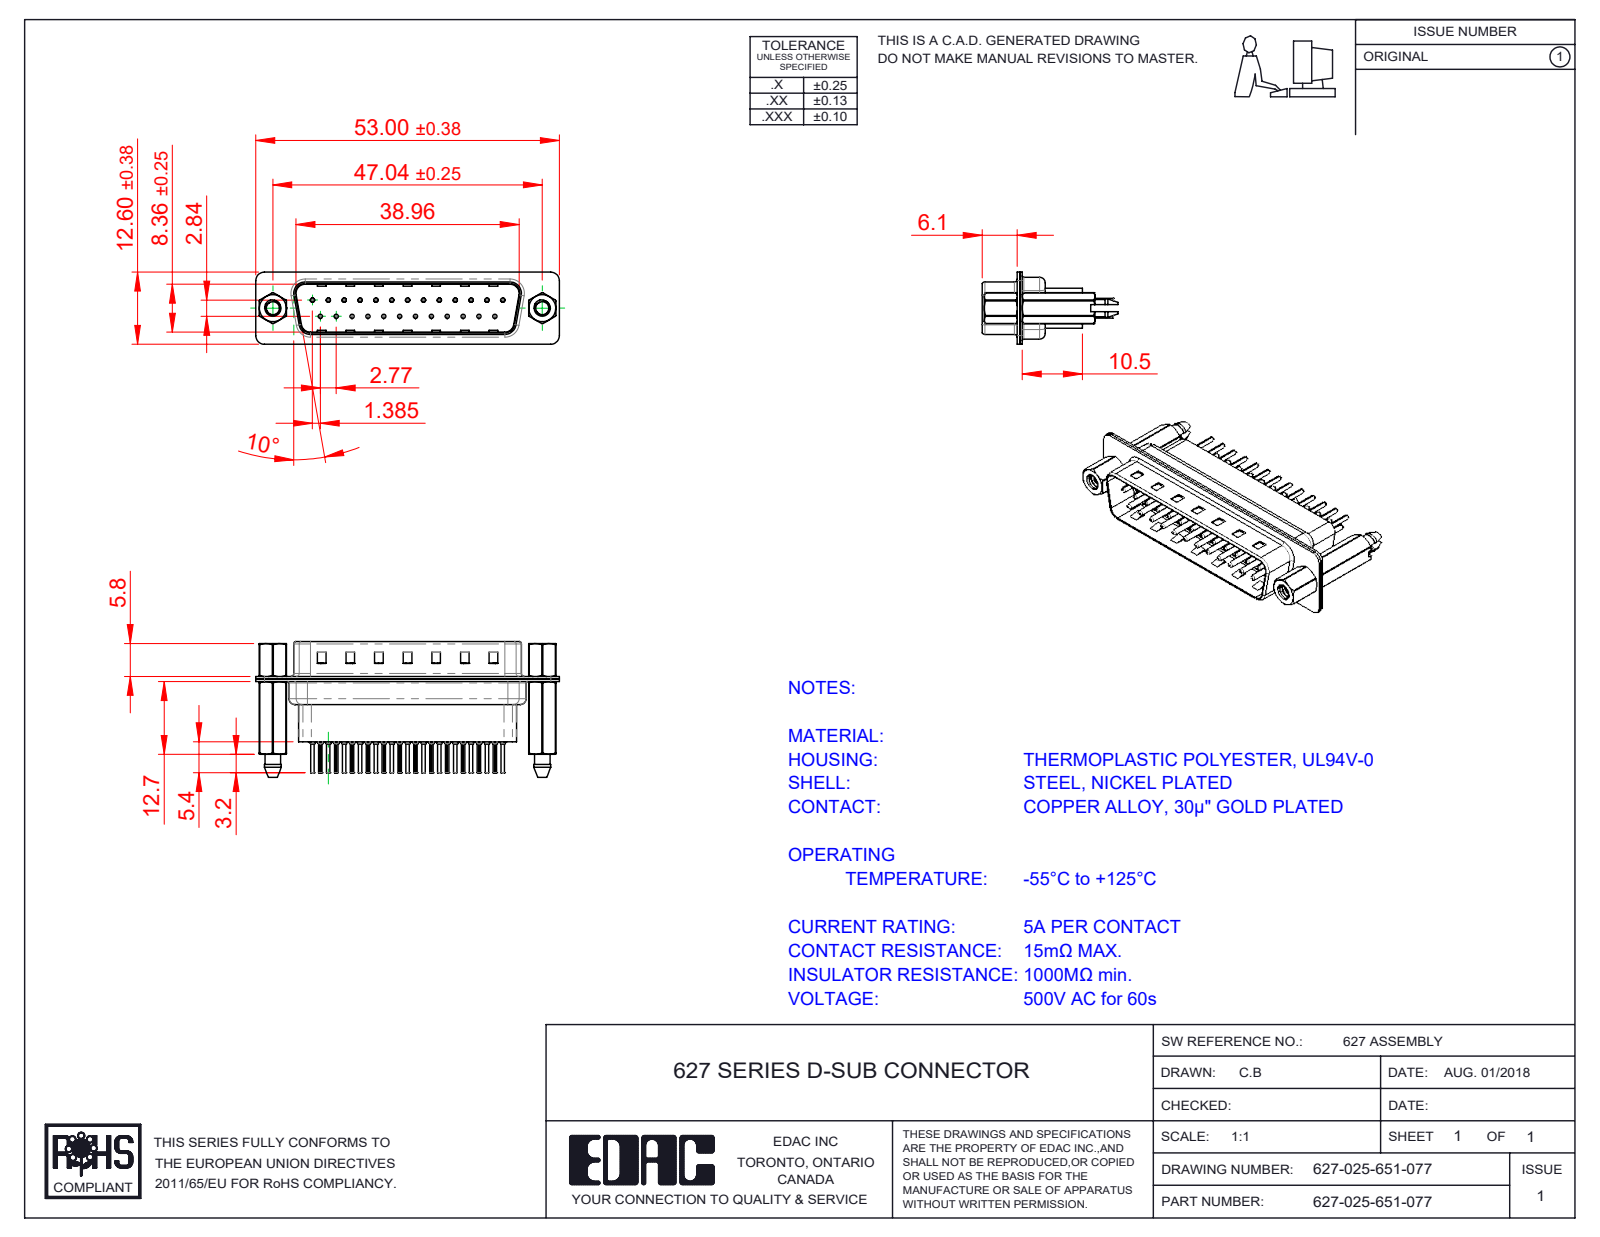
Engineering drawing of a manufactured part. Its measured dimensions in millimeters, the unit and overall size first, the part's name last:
Units: millimetres
Overall size (bounding box): 53 × 23.6 × 12.6
Round holes (diameter × count): ⌀0.2 ×25, ⌀0.35 ×25, ⌀1.1 ×25, ⌀1.6 ×25, ⌀2.26 ×2, ⌀2.29 ×2, ⌀4 ×2, ⌀4.8 ×2
Round bosses / shafts (diameter × count): ⌀2 ×25, ⌀1.5 ×25, ⌀0.75 ×25, ⌀0.6 ×25, ⌀4.9 ×2, ⌀2.79 ×2
Partial cylindrical surfaces — rounded edges, fillets, slot ends (radius × count): R0.1 ×50, R1.5 ×18, R2 ×12, R1.6 ×10, R0.5 ×8, R0.25 ×4, R0.6 ×4, R0.65 ×4
Main face-to-face distances: 0.4, 0.45, 0.82, 9.58, 0.68, 7.68, 1.5, 0.9, 1.08, 8.08
Hole centre spacings: 3.16, 8.31, 2.77, 5.54, 11.08, 16.62, 5.03, 5.04
Volume: 4 334 mm³ · Surface area: 11 076 mm²
Bodies: 32 solids, 3060 faces (825 planar, 1200 cylindrical, 1035 other)
Part name (STEP PRODUCT): 627 4-40 Threaded Boardlock_HP51; 627-025-651-077; 627 4-40 Hex Standoff; 627 Housing_25 HP (+4 more)
STEP written by: SolidWorks 2020 (CONFIG_CONTROL_DESIGN)
